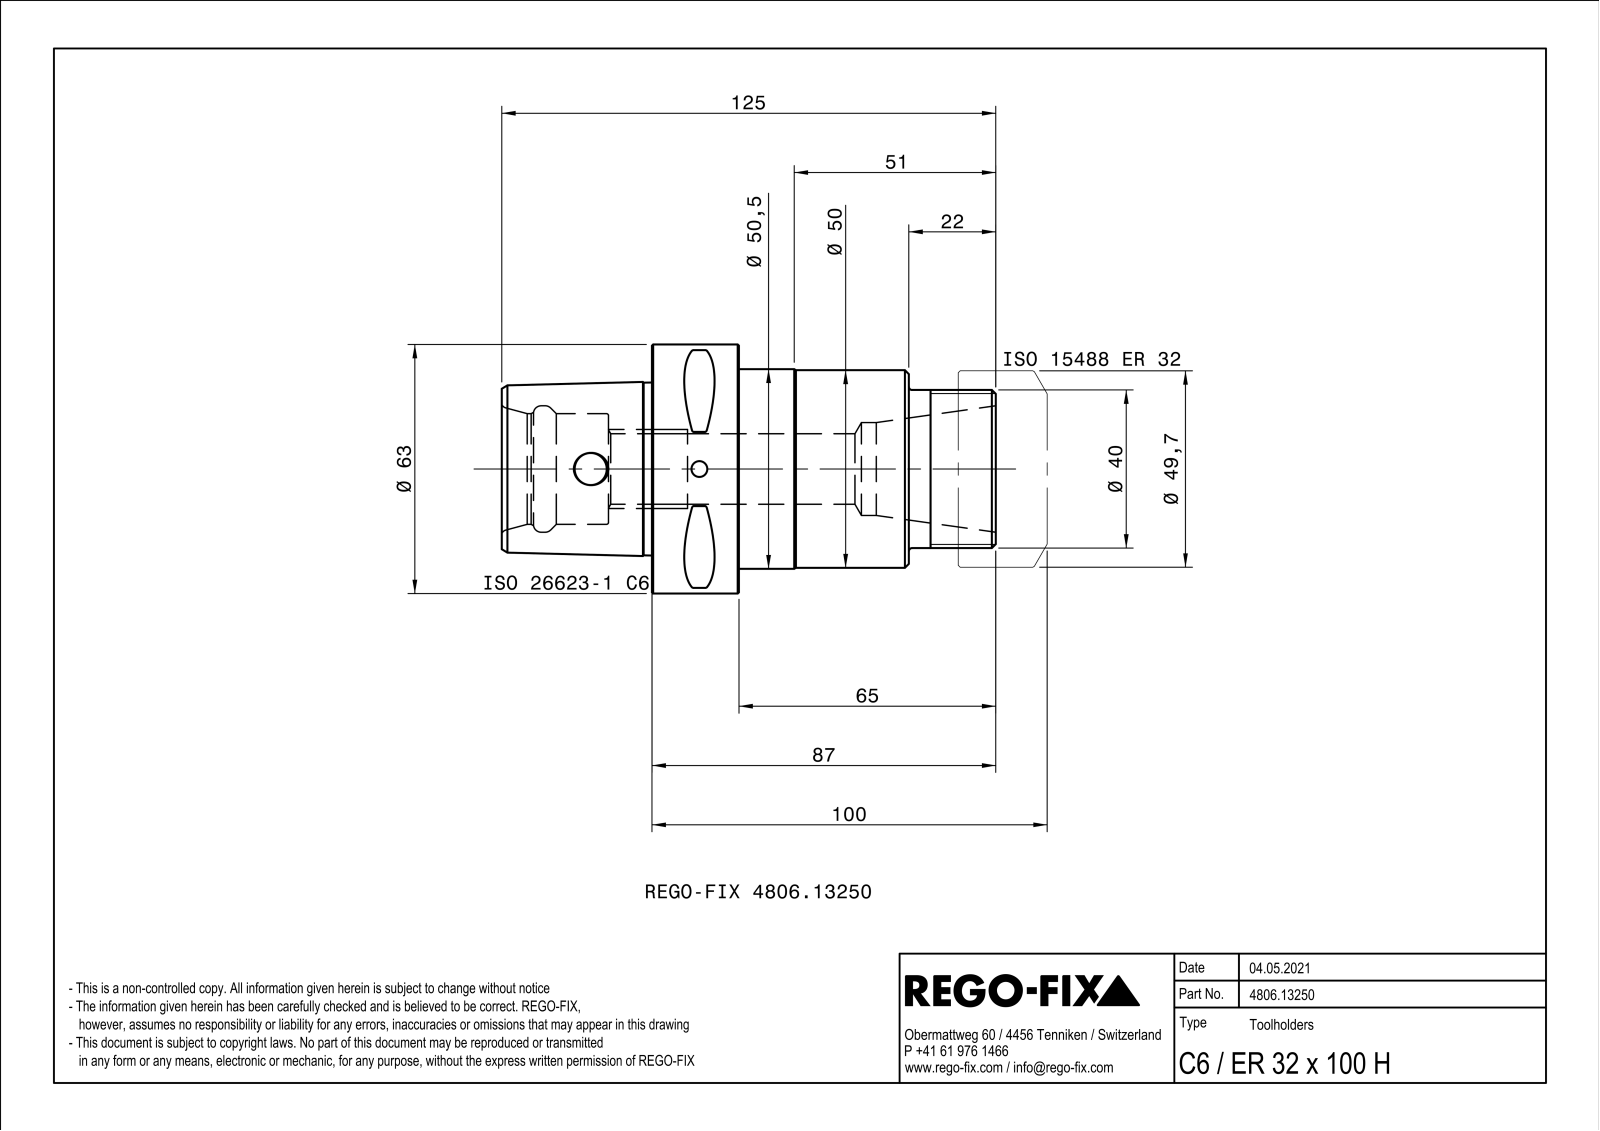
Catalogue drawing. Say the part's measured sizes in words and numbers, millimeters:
The part is named "NOCUT". Its 3-D file was written by "SIEMENS PLM Software Solid Edge ST10 (AUTOMOTIVE_DESIGN)". It is 1 solid with 125 faces: 22 planar, 26 cylindrical and 77 other. Overall it measures 125 by 63 by 63 millimeters. Its volume is 178 916 cubic millimeters and its surface area 33 445 square millimeters. Round holes: 1 of diameter 4, 1 of diameter 8.1, 1 of diameter 17.84, 1 of diameter 23.5, 1 of diameter 28, 1 of diameter 32. Round bosses or shafts: 1 of diameter 63, 1 of diameter 50.5, 1 of diameter 50, 1 of diameter 40. Partial cylindrical surfaces (rounded edges, fillets, slot ends): 8 of radius 0.5, 1 of radius 5. The main face-to-face distances are 22, 65, 43, 103, 60, 38, 87, 125, 24.89, 98. The hole center spacings are 27.5.
